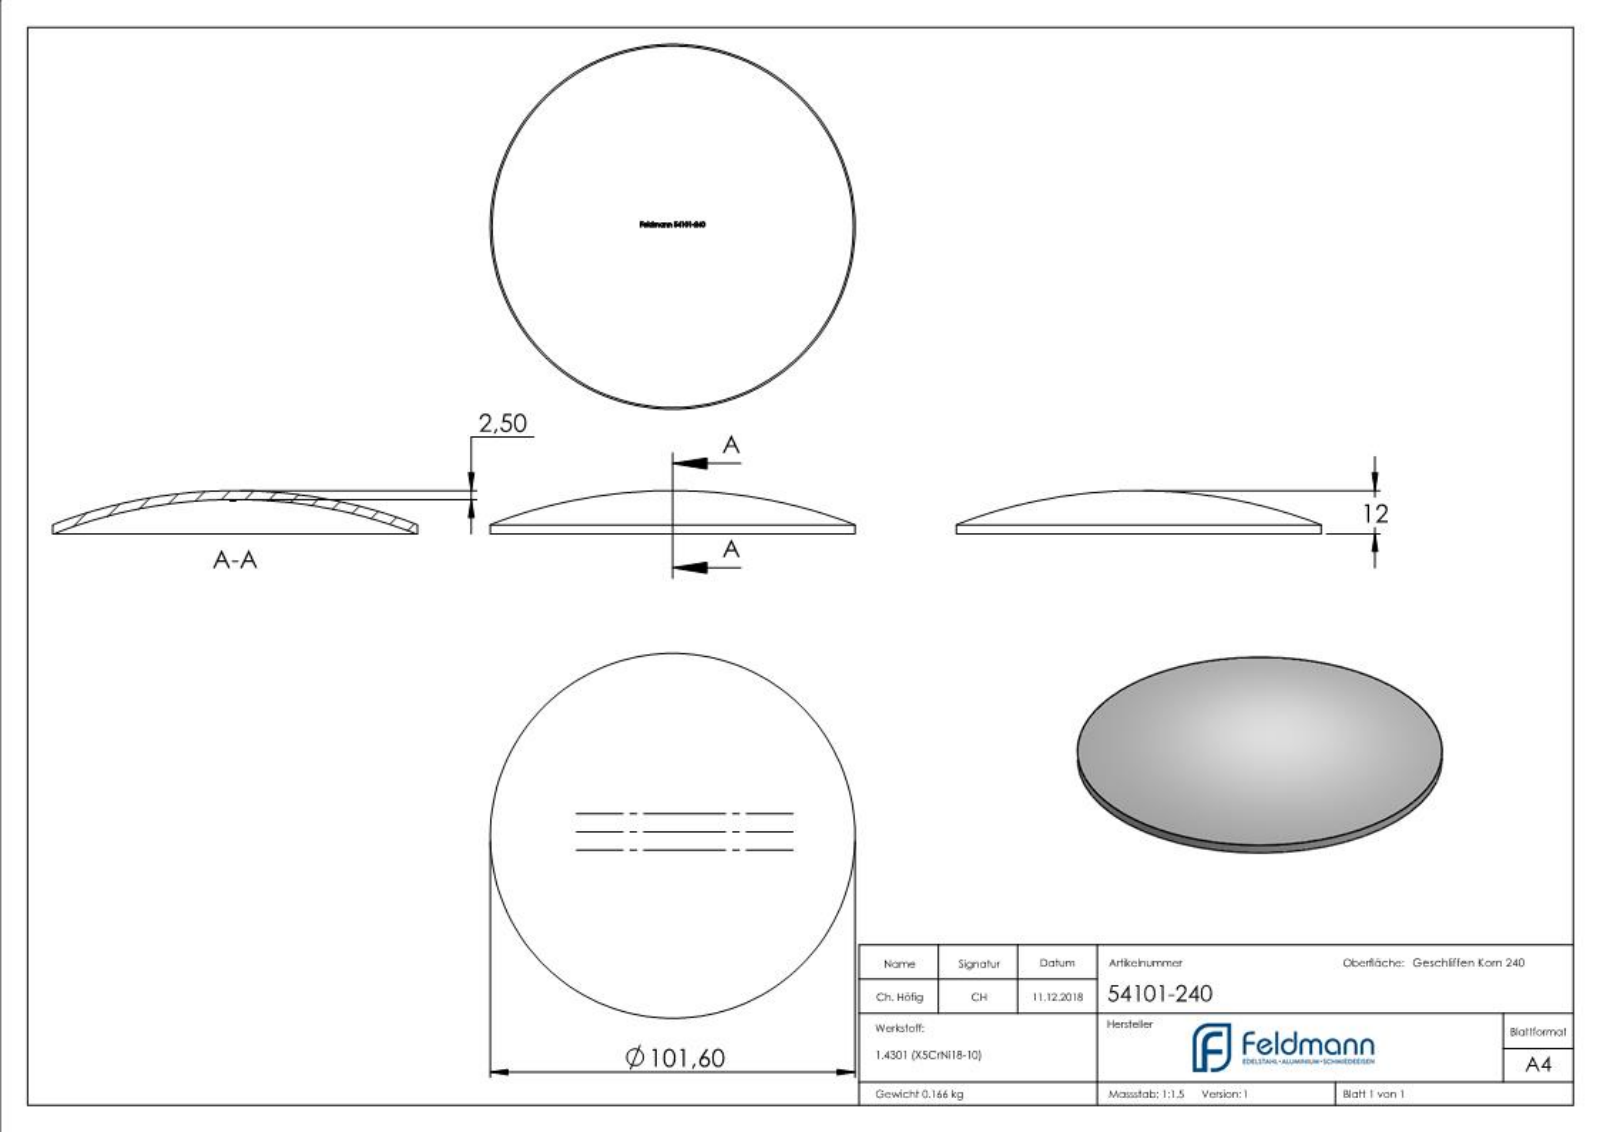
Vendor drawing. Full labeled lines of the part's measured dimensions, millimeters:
Part name (STEP PRODUCT): 54101-240
STEP written by: SolidWorks 2015 (CONFIG_CONTROL_DESIGN)
Units: millimetres
Bodies: 1 solid, 231 faces (109 planar, 2 cylindrical, 120 other)
Overall size (bounding box): 101.6 × 101.6 × 12
Volume: 20 977 mm³ · Surface area: 17 589 mm²
Round bosses / shafts (diameter × count): ⌀101.6 ×1
Main face-to-face distances: 0.88, 2.04, 0.44, 4.7, 11.73, 13.77, 1.32, 0.79, 2.83, 14.62
